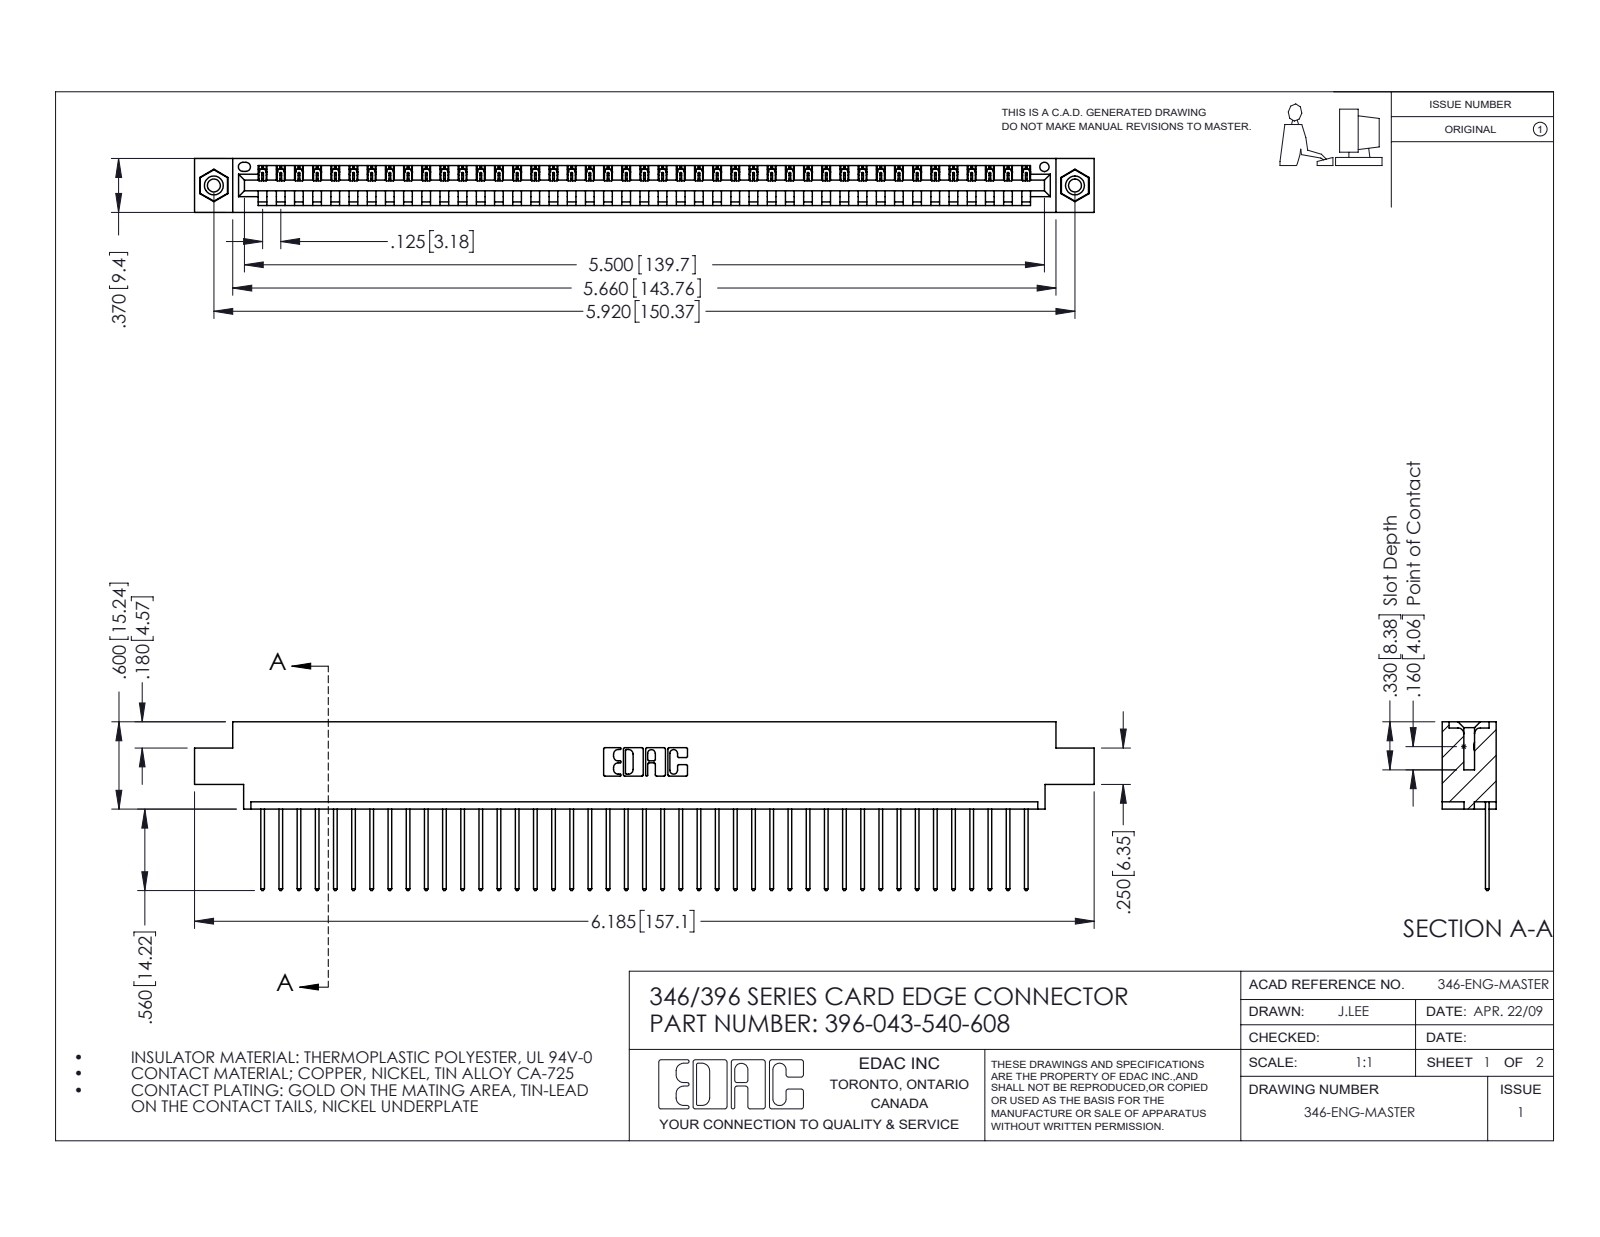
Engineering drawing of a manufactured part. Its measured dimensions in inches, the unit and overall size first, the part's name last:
Units: inches
Overall size (bounding box): 6.185 × 1.16 × 0.37
Round holes (diameter × count): ⌀0.089 ×2, ⌀0.125 ×2, ⌀0.156 ×2, ⌀0.064 ×1
Round bosses / shafts (diameter × count): ⌀0.155 ×2
Partial cylindrical surfaces — rounded edges, fillets, slot ends (radius × count): R0.006 ×86, R0.01 ×86, R0.01 ×22, R0.007 ×6, R0.031 ×6, R0.026 ×3, R0.031 ×2, R0.04 ×2
Main face-to-face distances: 0.048, 0.322, 0.37, 0.25, 0.072, 0.298, 0.025, 0.222, 0.148, 0.1
Hole centre spacings: 0.246, 5.711, 5.92
Volume: 0.912 in³ · Surface area: 29.9 in²
Bodies: 46 solids, 2680 faces (1832 planar, 832 cylindrical, 16 other)
Part name (STEP PRODUCT): 345-250-001_345-250-003-102; 345-292-001_345-293-140; 396-043-540-608; 346 Part_0.170 Offset - 0.156 Dia-TI
STEP written by: SolidWorks 2016 (CONFIG_CONTROL_DESIGN)
